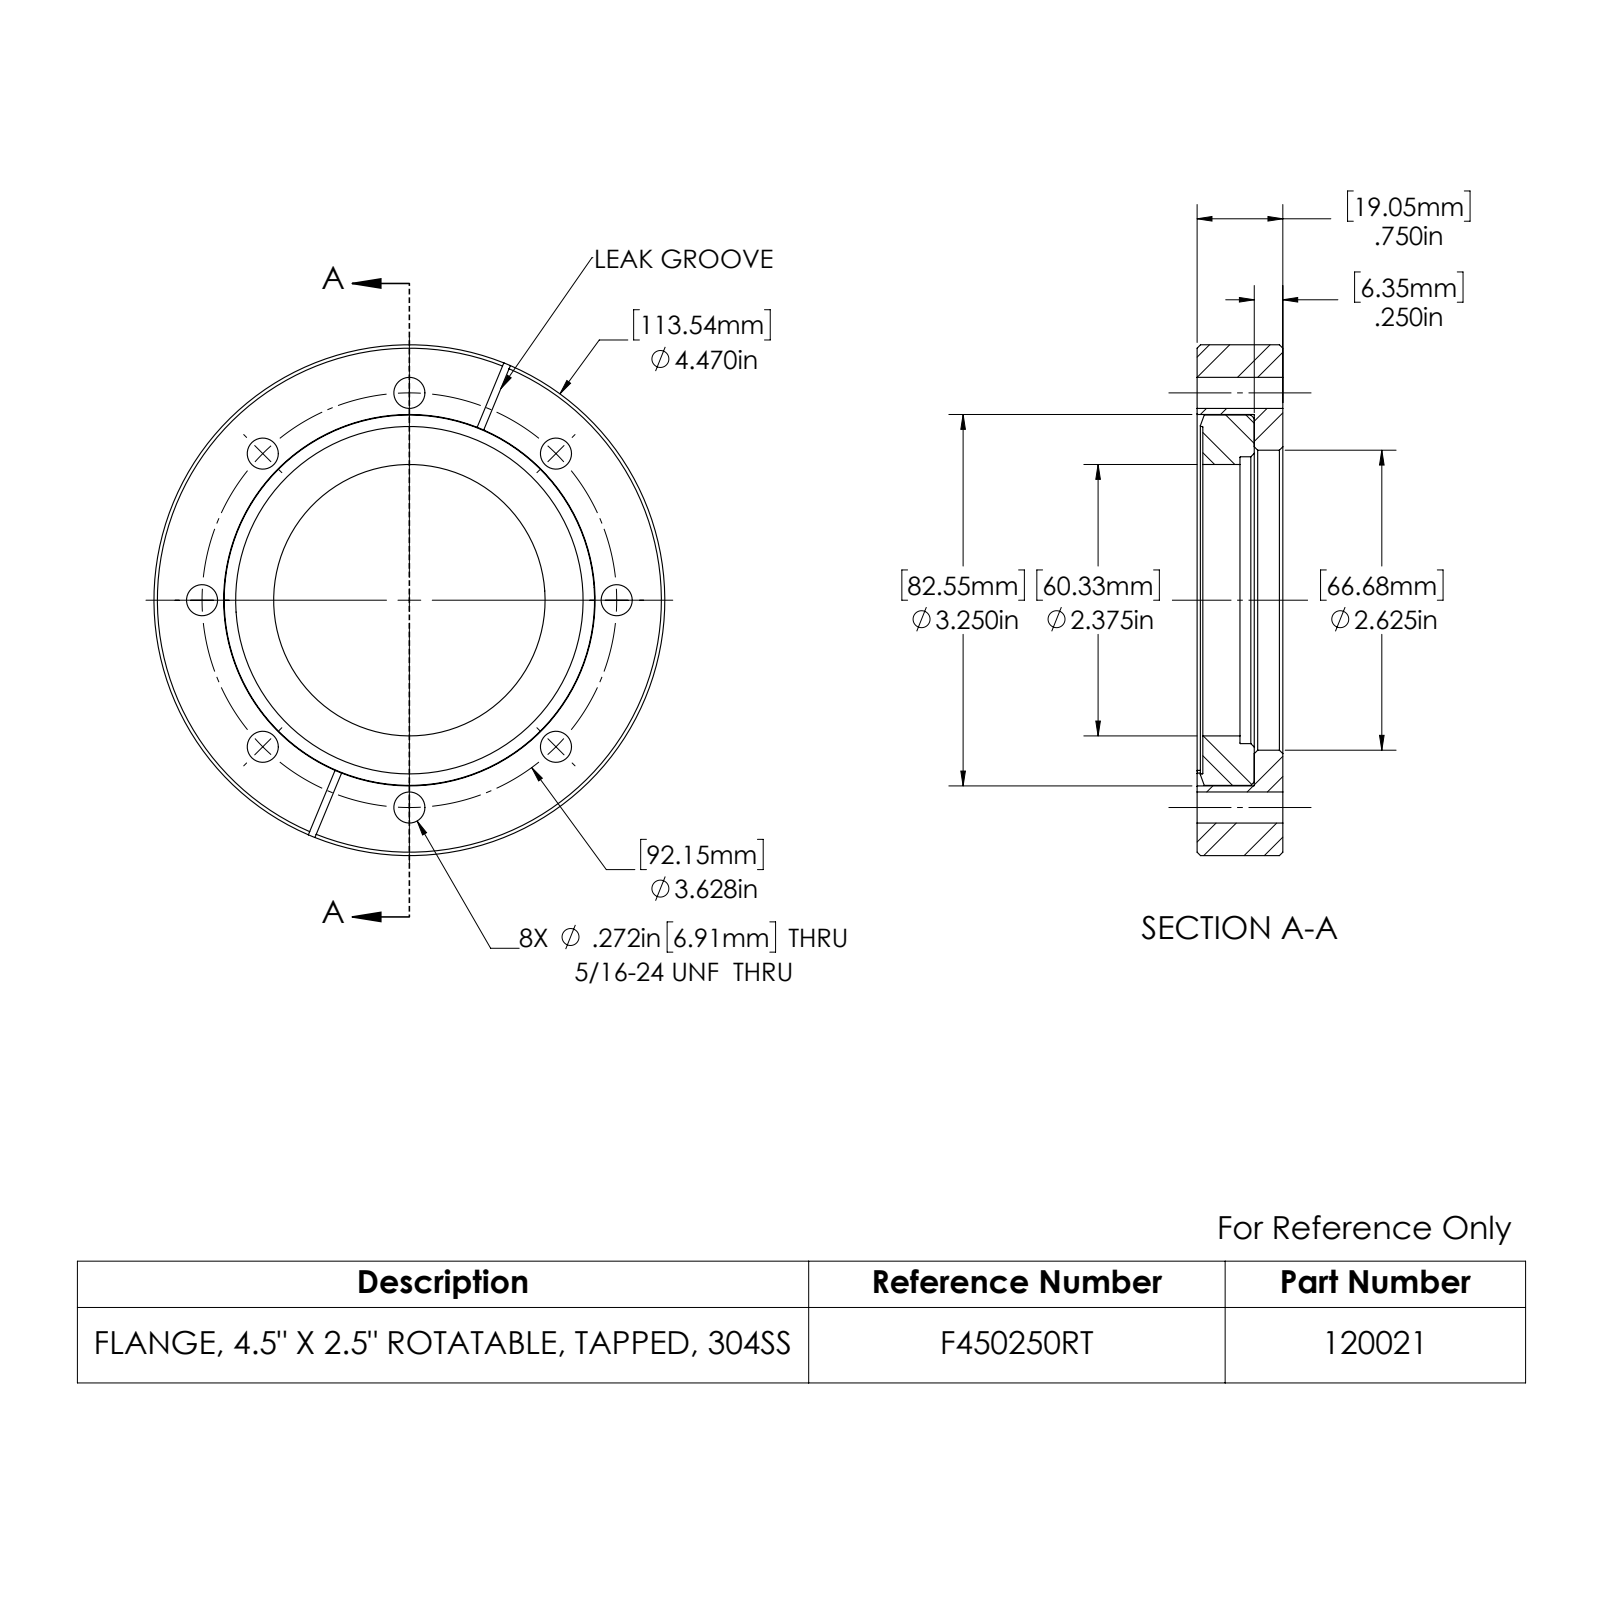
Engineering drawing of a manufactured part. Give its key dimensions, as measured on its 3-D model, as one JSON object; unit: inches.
{"part_name": "120021; 910021; 920004", "step_written_by": "SolidWorks 2022 (AUTOMOTIVE_DESIGN)", "units": "inches", "bodies": {"solids": 2, "faces": 69, "planar": 13, "cylindrical": 30, "other": 26}, "overall_size": [4.47, 4.47, 0.75], "volume_in3": 7.547, "surface_area_in2": 57.16, "round_holes": [[0.272, 8], [2.375, 1], [2.51, 1], [2.625, 1], [3.04, 1], [3.25, 1]], "round_bosses_or_shafts": [[4.47, 1], [3.241, 1]], "face_to_face_distances": [0.75, 0.5, 0.25, 0.05, 0.45, 0.7, 0.375, 0.325, 0.125, 0.375], "hole_center_spacings": [1.814, 2.565, 1.388, 1.389, 3.352, 3.352, 3.628, 1.814]}
